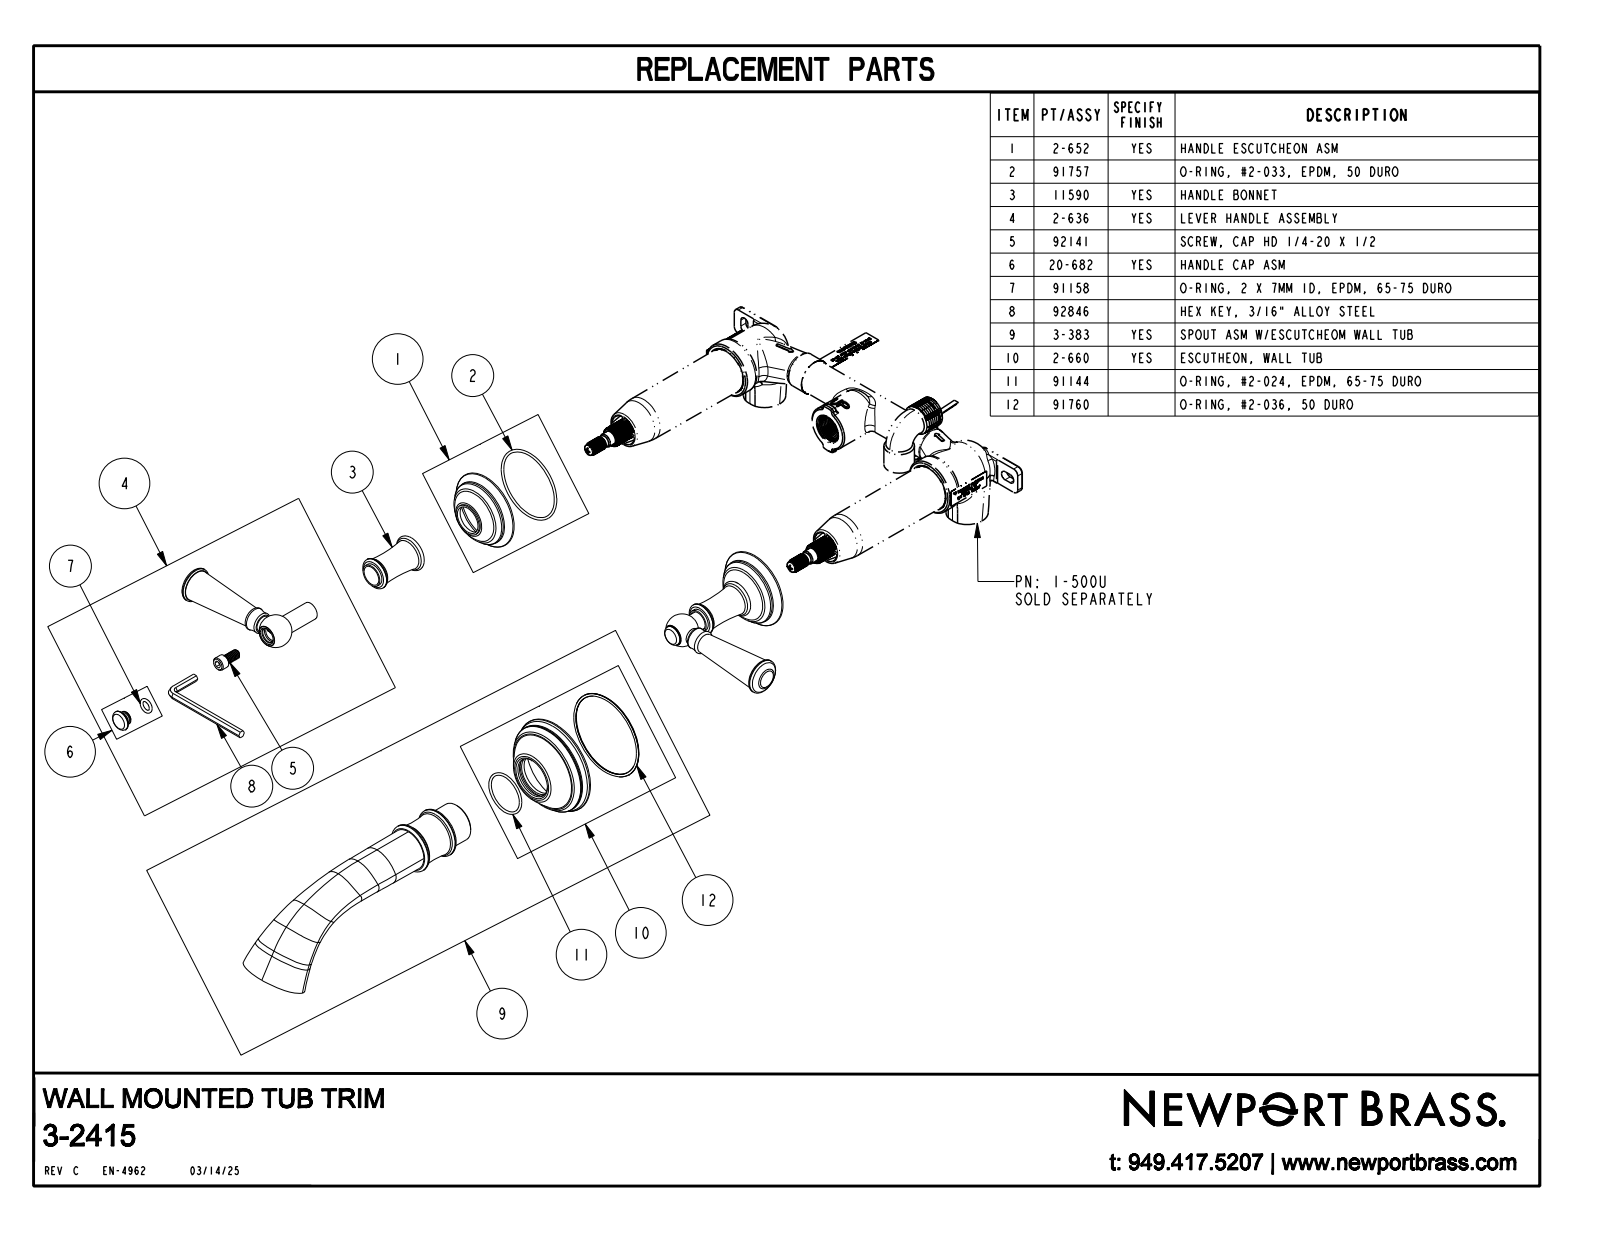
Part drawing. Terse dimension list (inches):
name: 3-2415_SW0001
written by: CREO PARAMETRIC BY PTC INC, 2018400 (AUTOMOTIVE_DESIGN)
unit: in
bodies: 3 solids, 221 faces (23 planar, 28 cylindrical, 170 other)
size: 14.475 × 8.901 × 7.825
volume: 20.21 in³; area: 91.36 in²
bosses: 2× ⌀0.9, 2× ⌀0.649, 2× ⌀0.56, 2× ⌀0.517, 1× ⌀1.4, 1× ⌀0.983, 1× ⌀0.461
face distances: 2.14, 2.22, 0.08, 0.481, 1.659, 1.739, 14.475, 0.925, 0.444, 1.215
